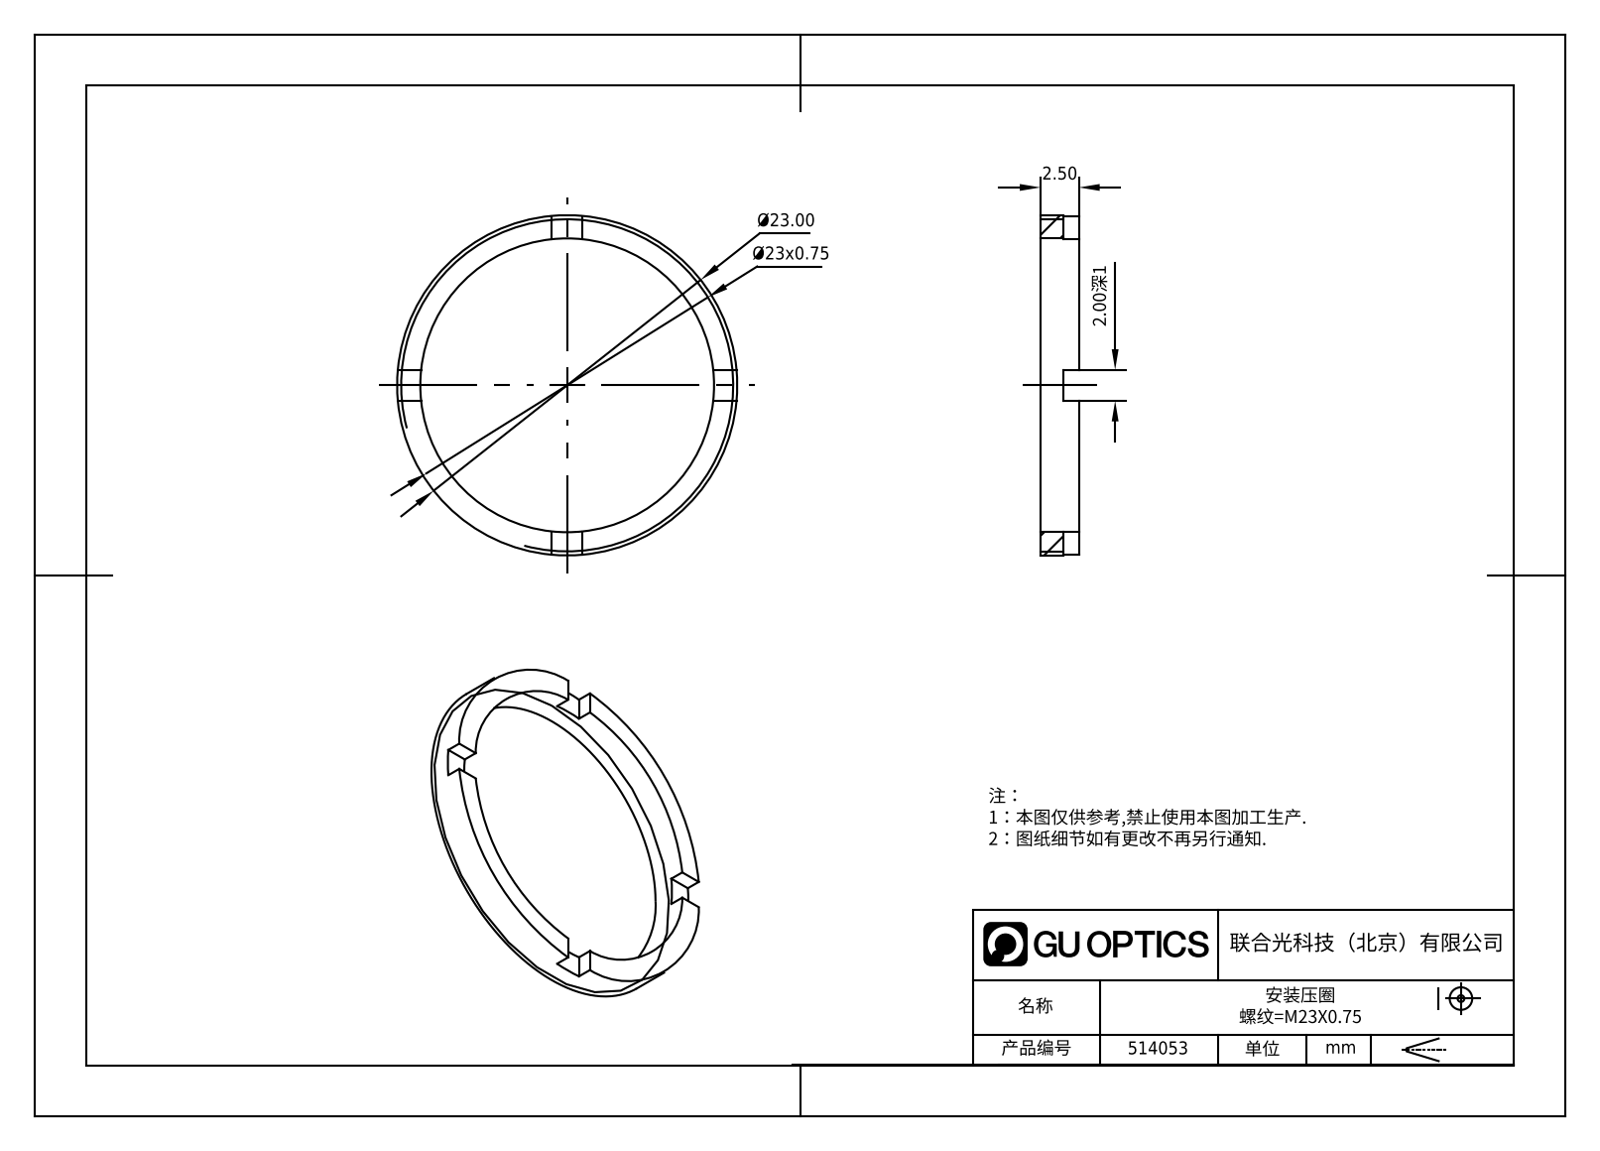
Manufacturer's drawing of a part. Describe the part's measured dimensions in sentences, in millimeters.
The part is named "514053". Its 3-D file was written by "SolidWorks 2020 (CONFIG_CONTROL_DESIGN)". It is 1 solid with 21 faces: 17 planar, 4 cylindrical and 0 other. Overall it measures 23 by 23 by 2.5 millimeters. Its volume is 241 cubic millimeters and its surface area 536 square millimeters. Round holes: 1 of diameter 20. Round bosses or shafts: 1 of diameter 23. The main face-to-face distances are 2.5, 1.5, 1, 2.
